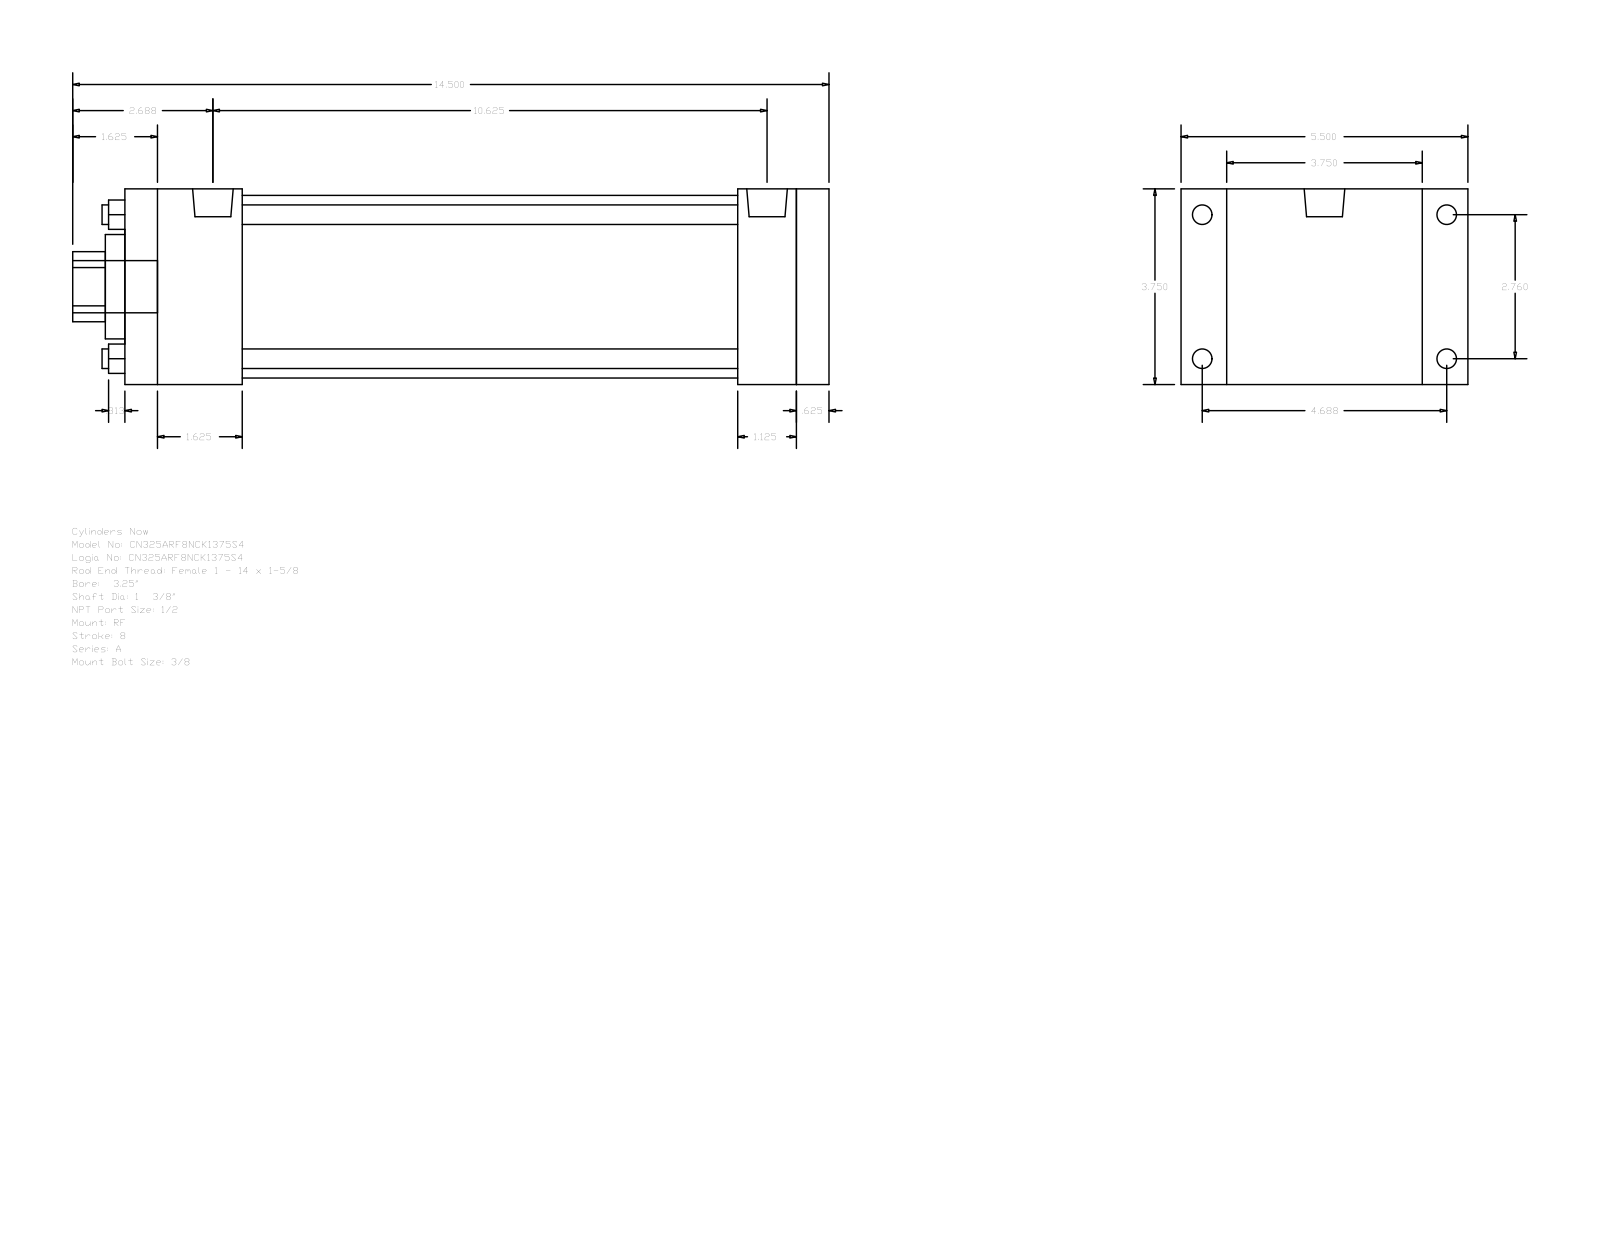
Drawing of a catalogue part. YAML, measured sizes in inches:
part_name: "A_RF__0325_1.375"
step_written_by: "GSSL Pune (CONFIG_CONTROL_DESIGN)"
units: inches
bodies: {solids: 0, faces: 92, planar: 64, cylindrical: 28, other: 0}
overall_size: [14.5, 5.5, 3.75]
round_holes:
  - {diameter: 0.375, count: 4}
  - {diameter: 1.375, count: 1}
  - {diameter: 2, count: 1}
  - {diameter: 3.5, count: 1}
round_bosses_or_shafts:
  - {diameter: 0.375, count: 4}
  - {diameter: 0.344, count: 4}
  - {diameter: 0.778, count: 2}
  - {diameter: 1, count: 1}
partial_cylinders:
  - {radius: 0.672, count: 1}
face_to_face_distances: [3.75, 13.5, 0.625, 12.875, 1.125, 0.875, 4.625, 11.75, 1.75, 2.25]
hole_center_spacings: [1.952, 2.76, 3.903]
